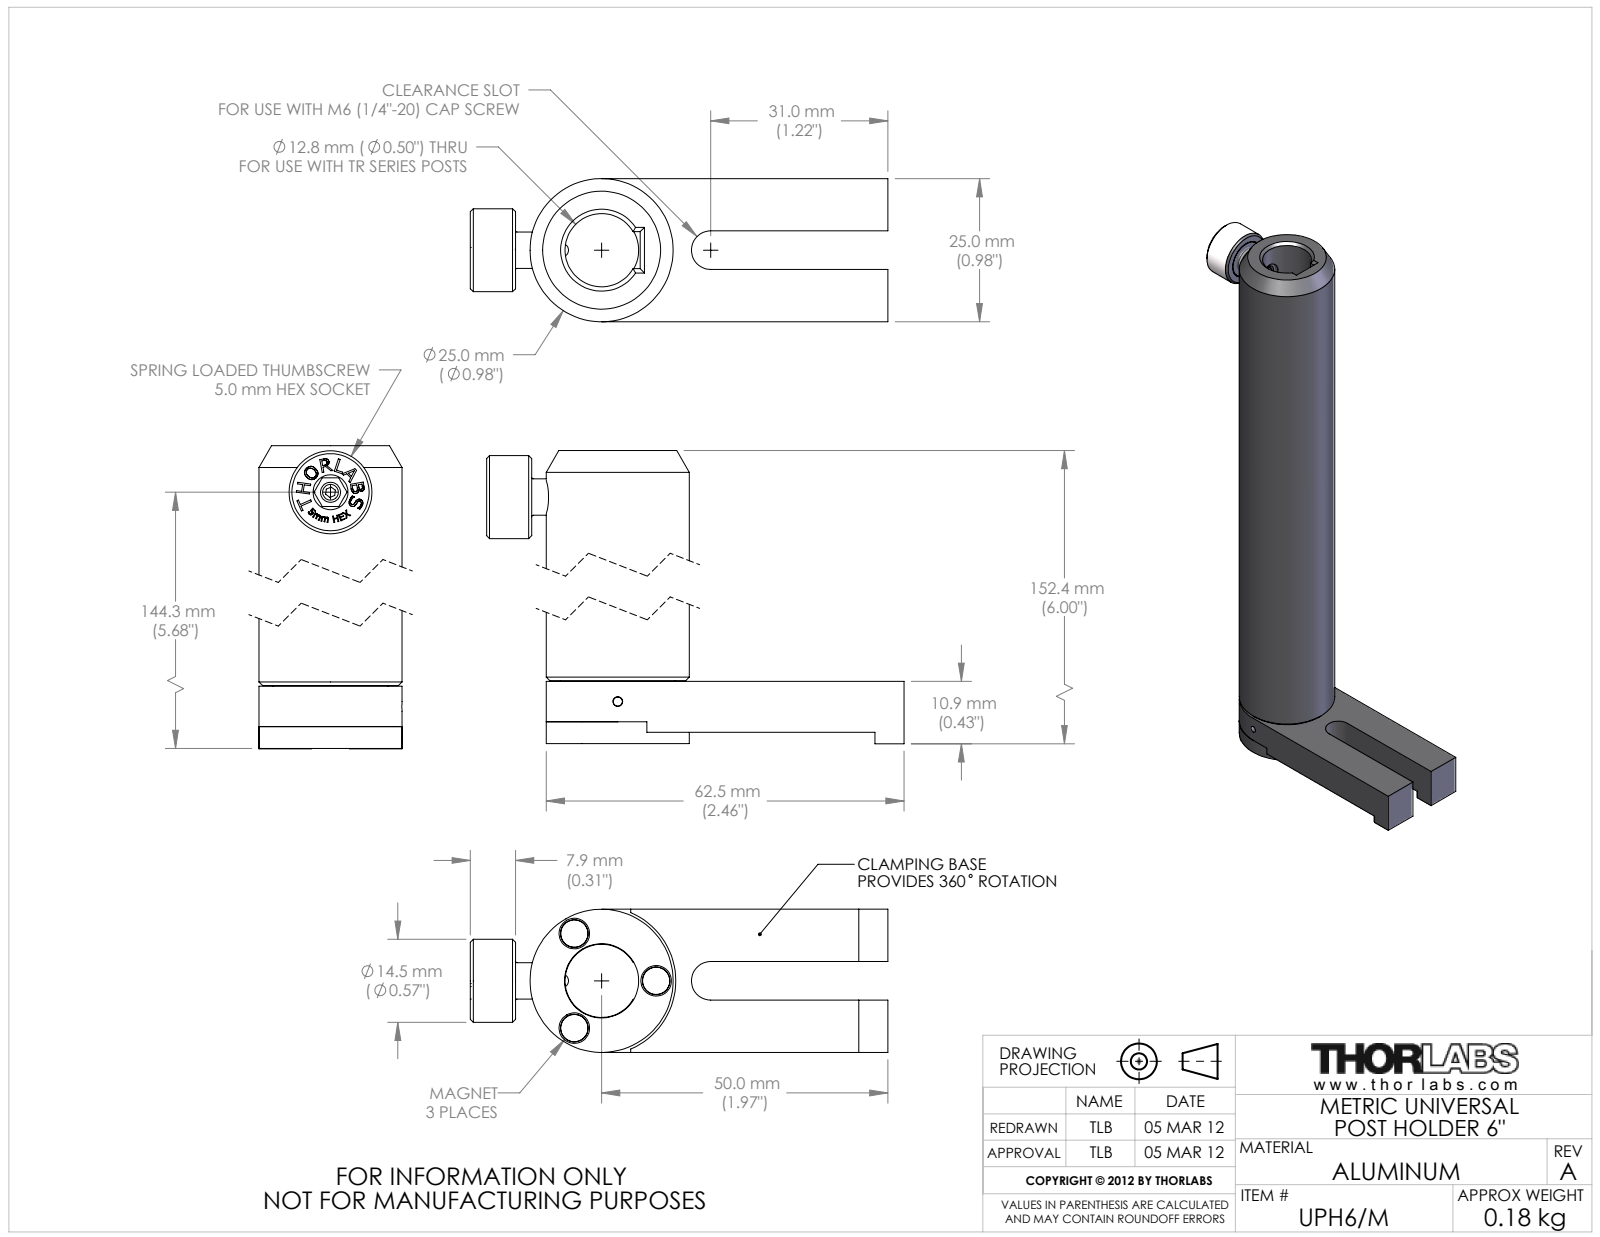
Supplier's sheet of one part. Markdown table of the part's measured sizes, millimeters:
| quantity | value |
| --- | --- |
| part name | 21067-E0W |
| STEP written by | SolidWorks 2011 (AUTOMOTIVE_DESIGN) |
| units | millimeters |
| bodies | 10 solids, 436 faces (211 planar, 84 cylindrical, 141 other) |
| overall size | 152.5 × 72.9 × 25 |
| volume | 62 470 mm³ |
| surface area | 26 390 mm² |
| round holes (diameter × count) | 4.8 × 3, 1.6 × 1, 1.7 × 1, 1.8 × 1, 2.1 × 1, 2.5 × 1, 3.2 × 1, 3.5 × 1, 5.1 × 1, 10.2 × 1, 12.8 × 1, 13 × 1 |
| round bosses / shafts (diameter × count) | 4.7 × 3, 25 × 1, 20.1 × 1, 17.8 × 1, 17.3 × 1, 14.5 × 1, 9.9 × 1, 6.4 × 1 |
| partial cylindrical surfaces (radius × count) | 3.4 × 1, 13 × 1 |
| main face-to-face distances | 8.9, 9.1, 15.9, 25, 1.8, 7.1, 2, 3.8, 10.9, 9.3 |
| hole center spacings | 9.5, 16.5, 16.5 |
